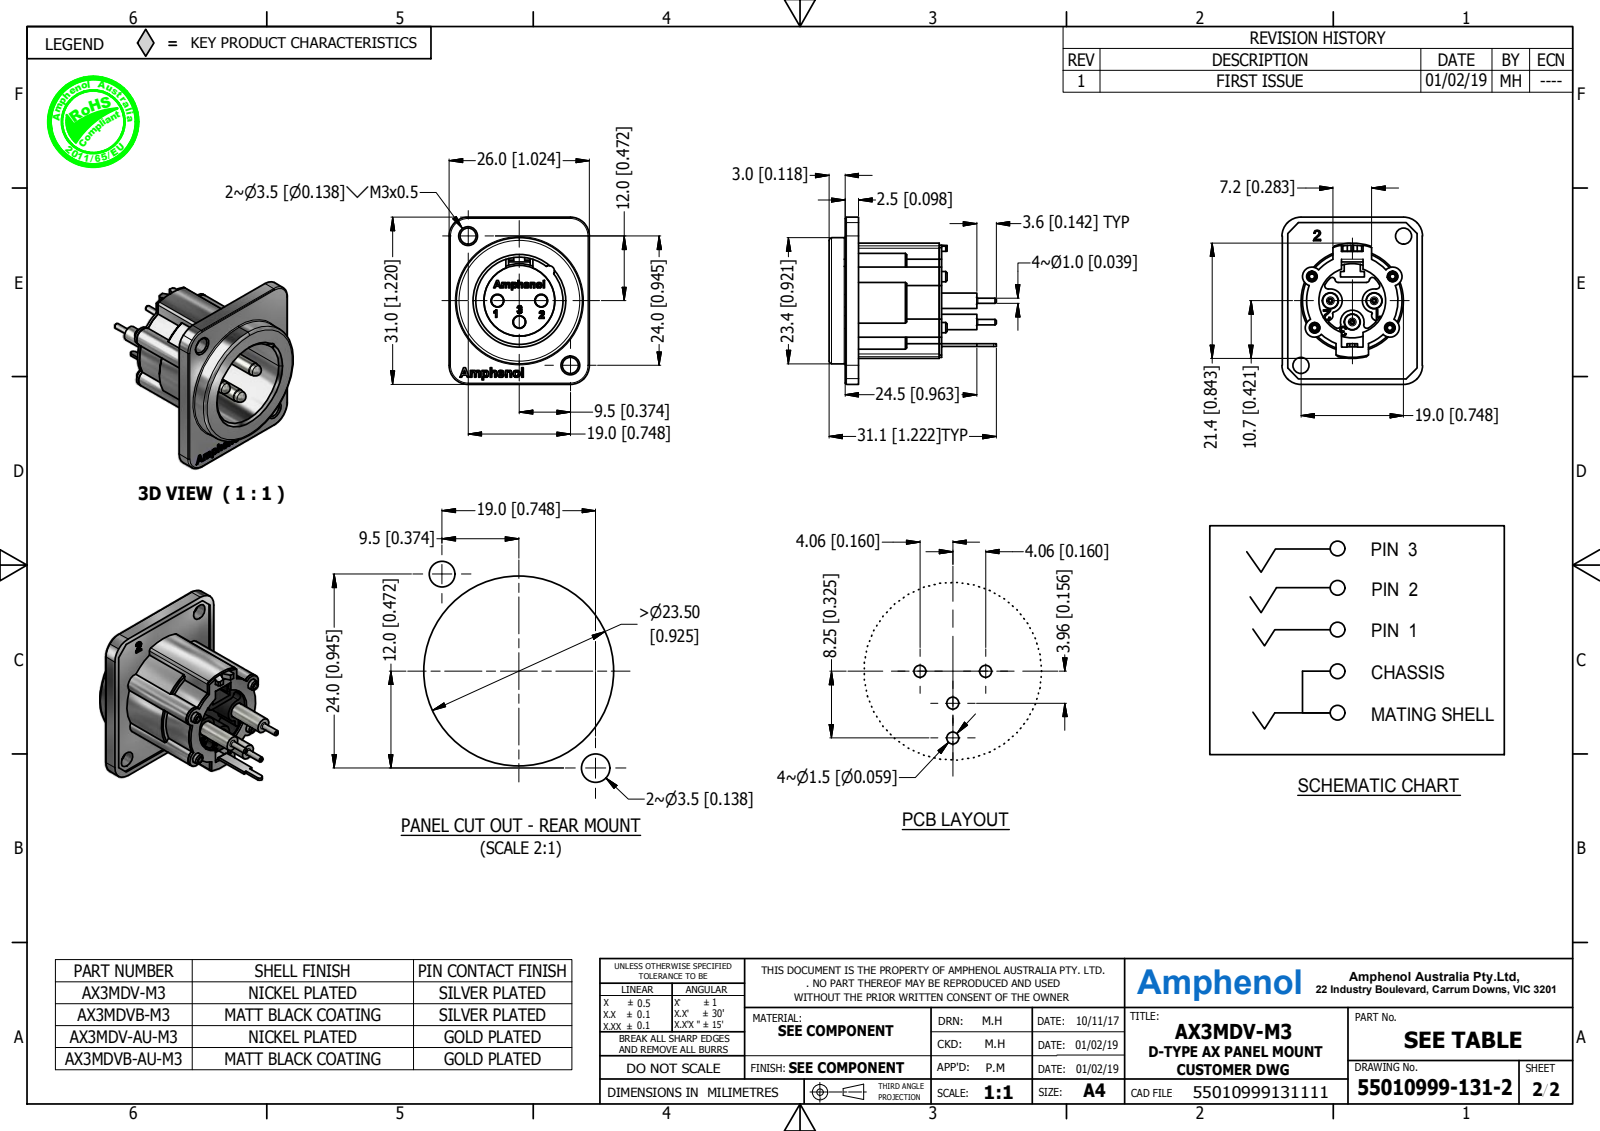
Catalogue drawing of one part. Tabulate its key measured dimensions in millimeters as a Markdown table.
| quantity | value |
| --- | --- |
| part name | AX3MDV-M3_Shrinkwrap_1 |
| STEP written by | Autodesk Inventor 2016 (AUTOMOTIVE_DESIGN) |
| units | millimeters |
| bodies | 0 solids, 293 faces (125 planar, 108 cylindrical, 60 other) |
| overall size | 31.05 × 31 × 26 |
| round holes (diameter × count) | 1 × 4, 3 × 2, 16.2 × 1 |
| round bosses / shafts (diameter × count) | 1.9 × 4, 2.85 × 3, 2.37 × 3, 1 × 3, 23.4 × 1, 13.8 × 1 |
| partial cylindrical surfaces (radius × count) | 0.5 × 7, 0.6 × 6, 0.25 × 4, 1.75 × 4, 3.5 × 4, 2.2 × 3, 0.95 × 2, 5 × 2 |
| main face-to-face distances | 10.5, 2.2, 15.25, 17.45, 0.5, 3, 13.5, 6.95, 8.3, 2.5 |
| hole center spacings | 8.6, 8.75, 9.51, 15.31, 17.33, 23.69, 7.43, 7.76 |
